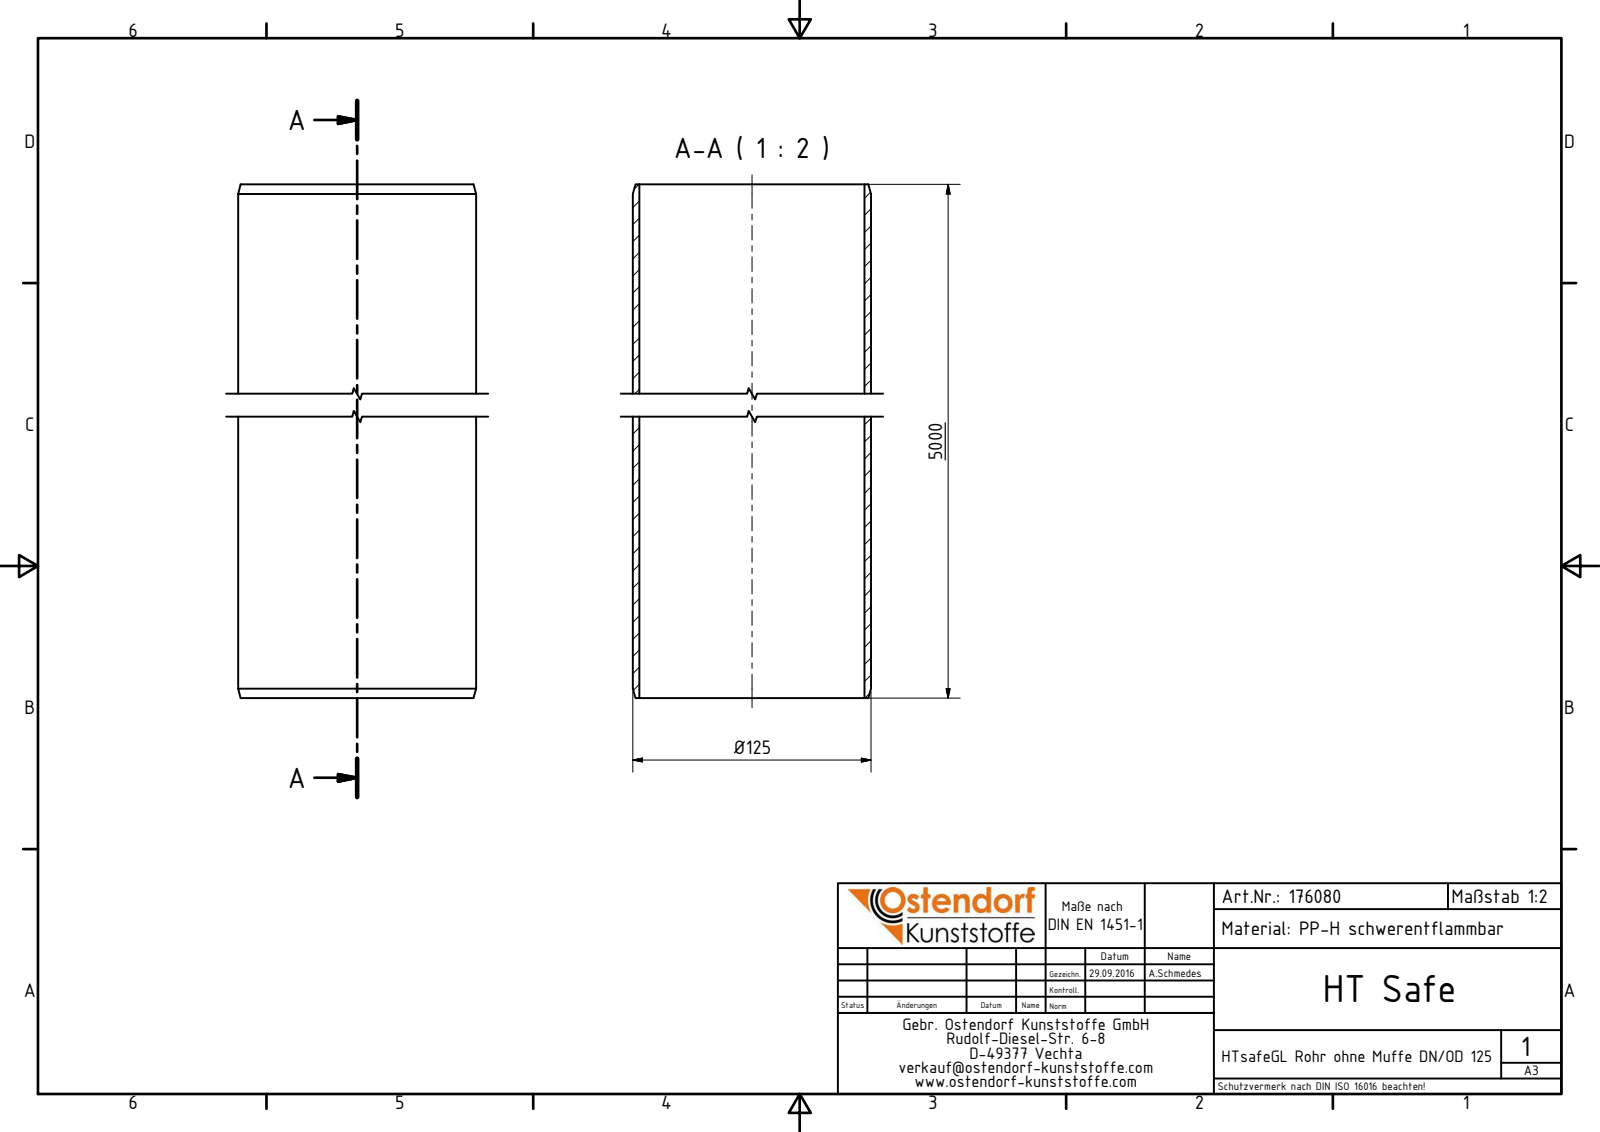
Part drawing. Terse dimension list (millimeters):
name: 176080 HTsafeGL DN_OD 125x5000
written by: Autodesk Inventor 2016 (AUTOMOTIVE_DESIGN)
unit: mm
bodies: 1 solid, 6 faces (2 planar, 2 cylindrical, 2 other)
size: 5000 × 125 × 125
volume: 6 492 000 mm³; area: 3 822 000 mm²
holes: 1× ⌀118.2
bosses: 1× ⌀125
face distances: 5000
